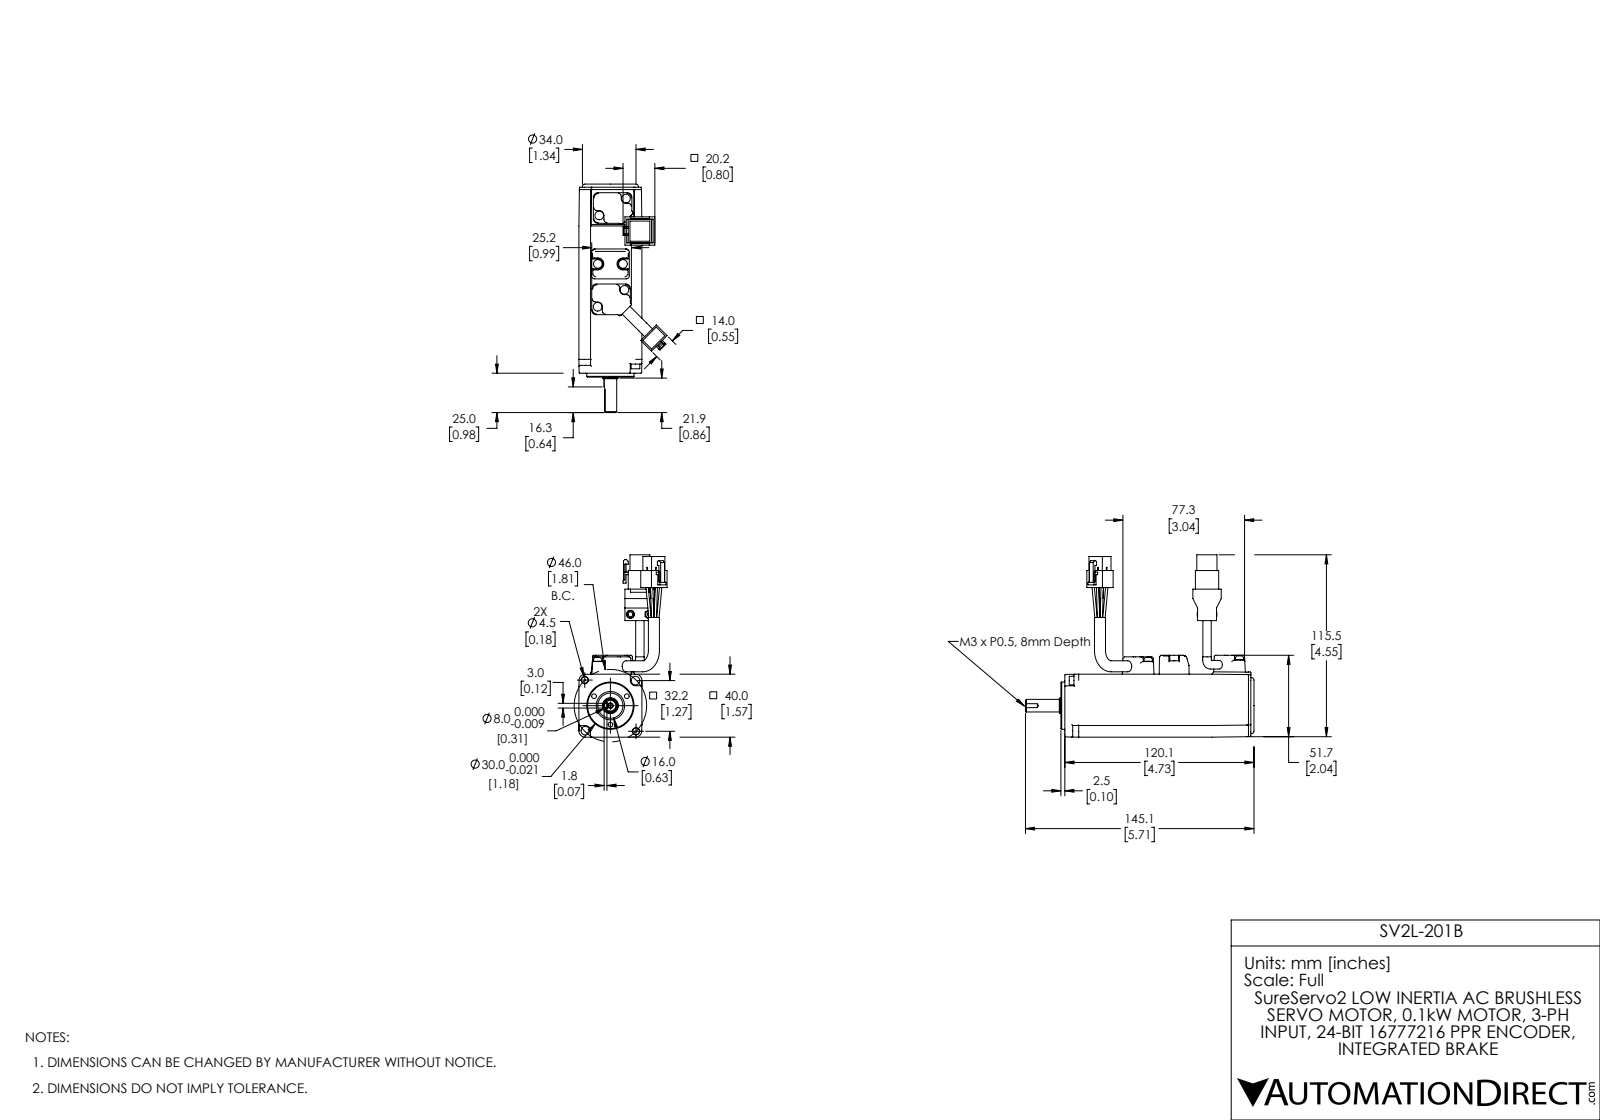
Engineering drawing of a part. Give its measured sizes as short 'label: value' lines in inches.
name: ECM-A3H-CX0401SSX 201B red1 Coord
written by: SolidWorks 2017 (AUTOMOTIVE_DESIGN)
unit: in
bodies: 2 solids, 685 faces (291 planar, 232 cylindrical, 162 other)
size: 5.713 × 4.559 × 2.203
volume: 12.78 in³; area: 51.34 in²
holes: 3× ⌀0.118, 2× ⌀0.201, 1× ⌀0.098, 1× ⌀0.63, 1× ⌀0.709
bosses: 10× ⌀0.217, 6× ⌀0.059, 4× ⌀0.181, 2× ⌀0.276, 2× ⌀0.197, 2× ⌀0.098, 1× ⌀1.398, 1× ⌀1.181
rounds: 48× R0.02, 38× R0.039, 12× R0.079, 11× R0.008, 6× R0.11, 5× R0.03, 4× R0.157, 2× R0.031
face distances: 1.575, 0.291, 1.283, 0.472, 0.039, 4.728, 0.079, 2.047, 0.043, 0.083
hole spacings: 0.472, 0.818, 2.049, 2.124, 2.24, 2.338, 2.47, 2.482
